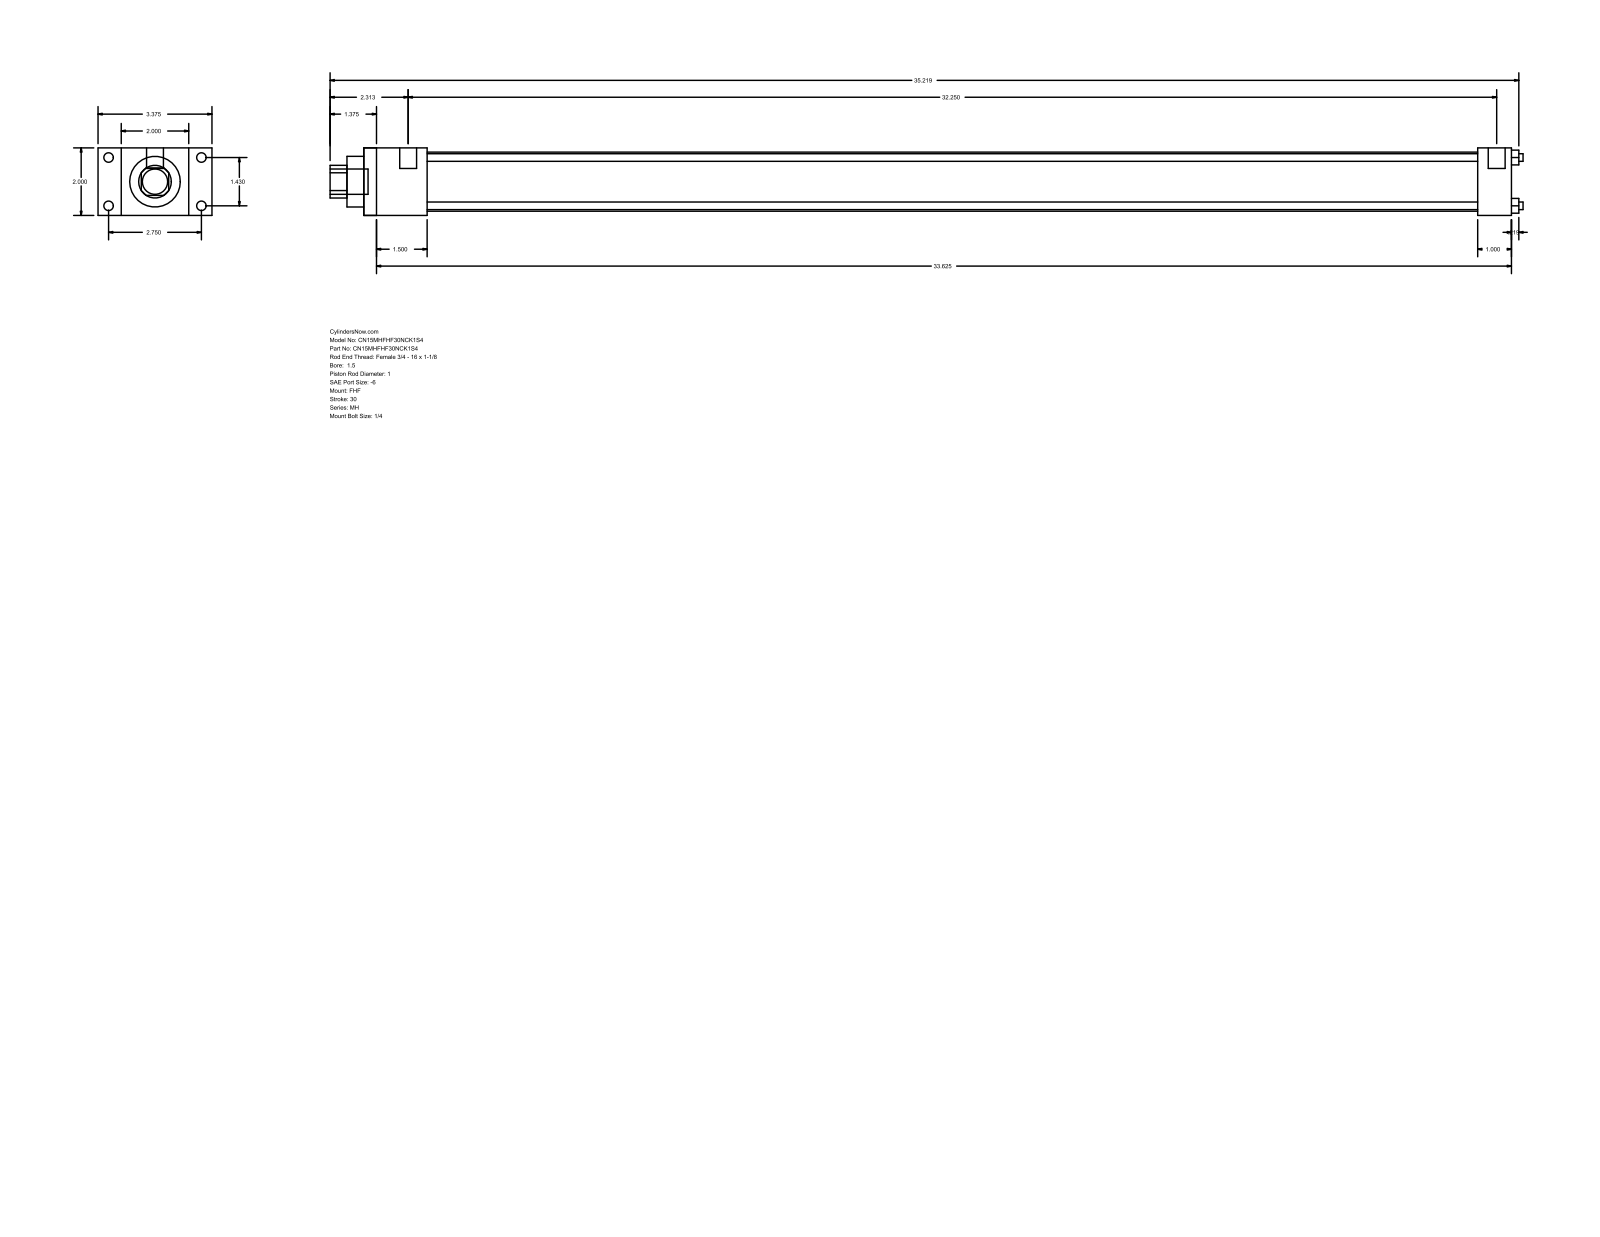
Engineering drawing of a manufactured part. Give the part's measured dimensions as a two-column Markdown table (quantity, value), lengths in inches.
| quantity | value |
| --- | --- |
| part name | MH_FHF__0150_1 |
| STEP written by | GSSL Pune (CONFIG_CONTROL_DESIGN) |
| units | inches |
| bodies | 0 solids, 88 faces (60 planar, 28 cylindrical, 0 other) |
| overall size | 35.344 × 3.375 × 2 |
| round holes (diameter × count) | 0.225 × 4, 1 × 1, 1.5 × 1, 1.75 × 1 |
| round bosses / shafts (diameter × count) | 0.281 × 4, 0.219 × 4, 0.5 × 2, 0.75 × 1 |
| partial cylindrical surfaces (radius × count) | 0.484 × 1 |
| main face-to-face distances | 2, 0.687, 2.687, 1.875, 3.375, 34, 32.125, 1, 33, 31.125 |
| hole center spacings | 1.011, 1.43, 2.022 |
